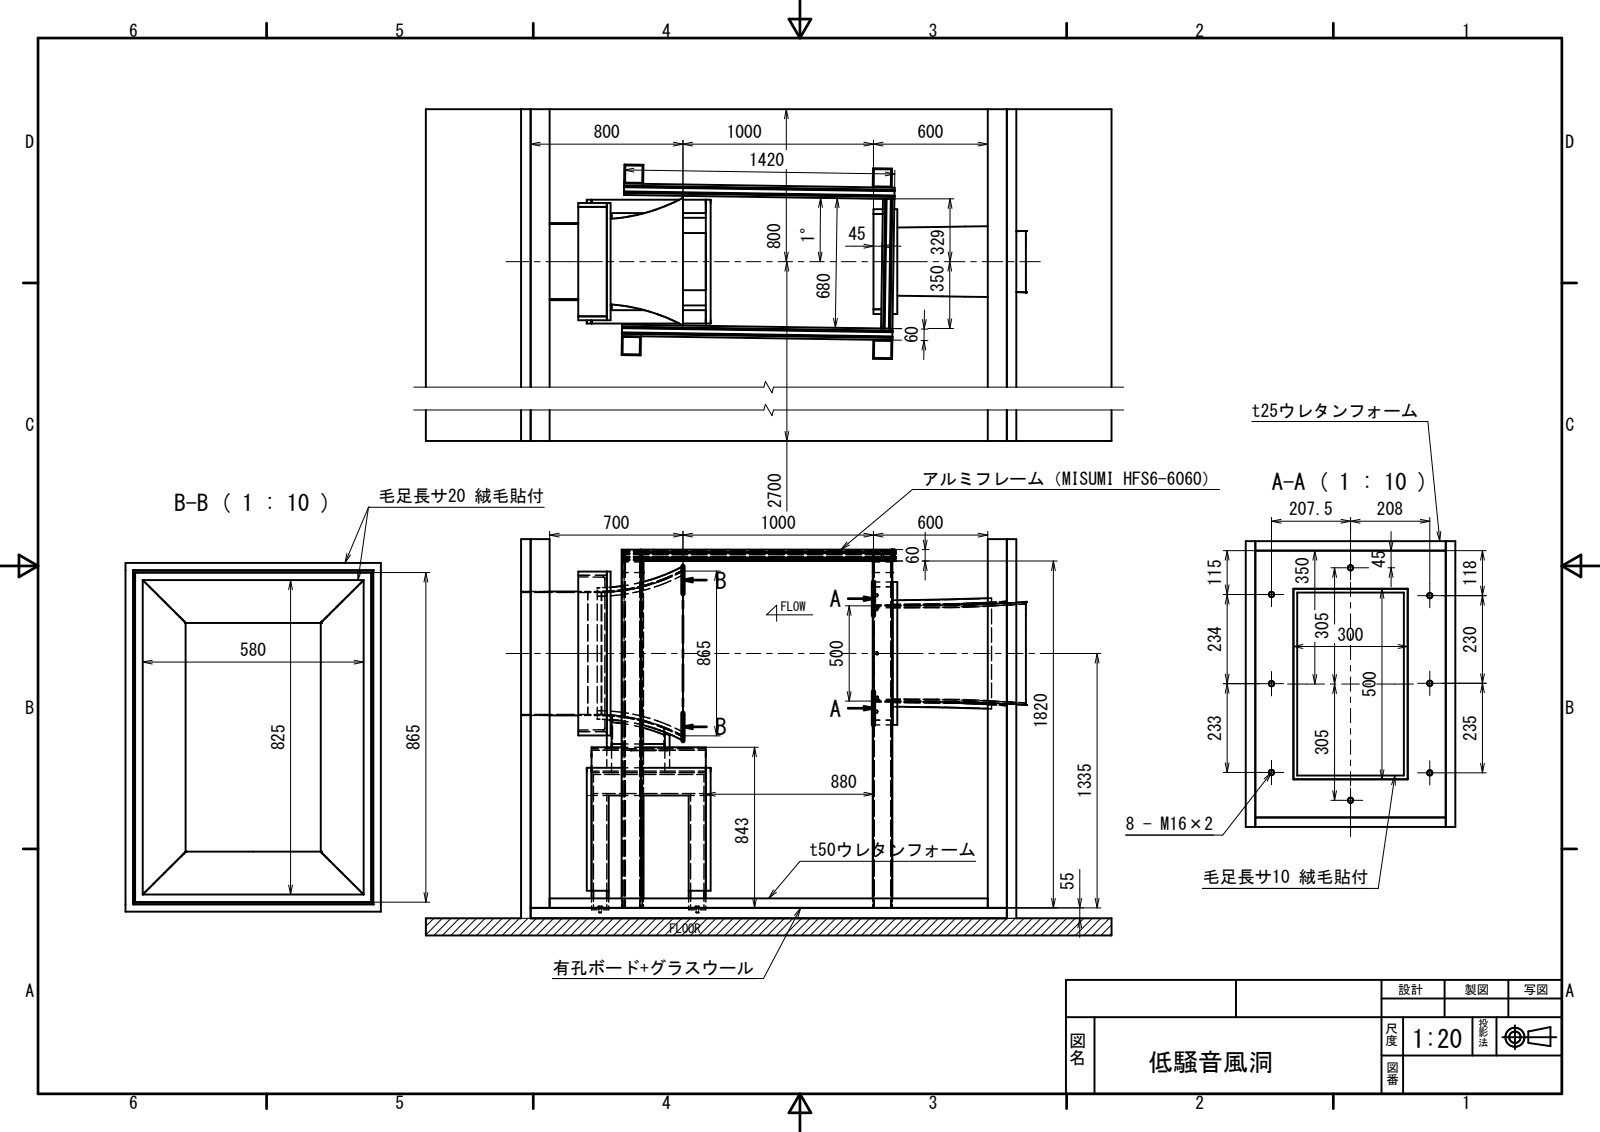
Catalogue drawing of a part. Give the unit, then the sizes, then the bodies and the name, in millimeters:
Units: millimetres
Overall size (bounding box): 3600 × 3500 × 2080
Round holes (diameter × count): ⌀13.84 ×8, ⌀14 ×6
Round bosses / shafts (diameter × count): ⌀18 ×4, ⌀12 ×4
Partial cylindrical surfaces — rounded edges, fillets, slot ends (radius × count): R0.5 ×48, R1 ×48, R10 ×14, R2 ×12, R3.4 ×12, R6 ×12, R9 ×6, R20 ×6
Main face-to-face distances: 50, 55, 100, 2450, 150, 2550, 2400, 90, 2500, 145
Hole centre spacings: 415.5, 476.86, 510, 576, 769.33, 133.54, 180, 218.99
Volume: 4 219 000 000 mm³ · Surface area: 153 300 000 mm²
Bodies: 57 solids, 1373 faces (927 planar, 216 cylindrical, 230 other)
Part name (STEP PRODUCT): GL; GL_1; nozzle_front; nozzle_ver2_1 (+8 more)
STEP written by: Autodesk Inventor 2016 (AUTOMOTIVE_DESIGN)
